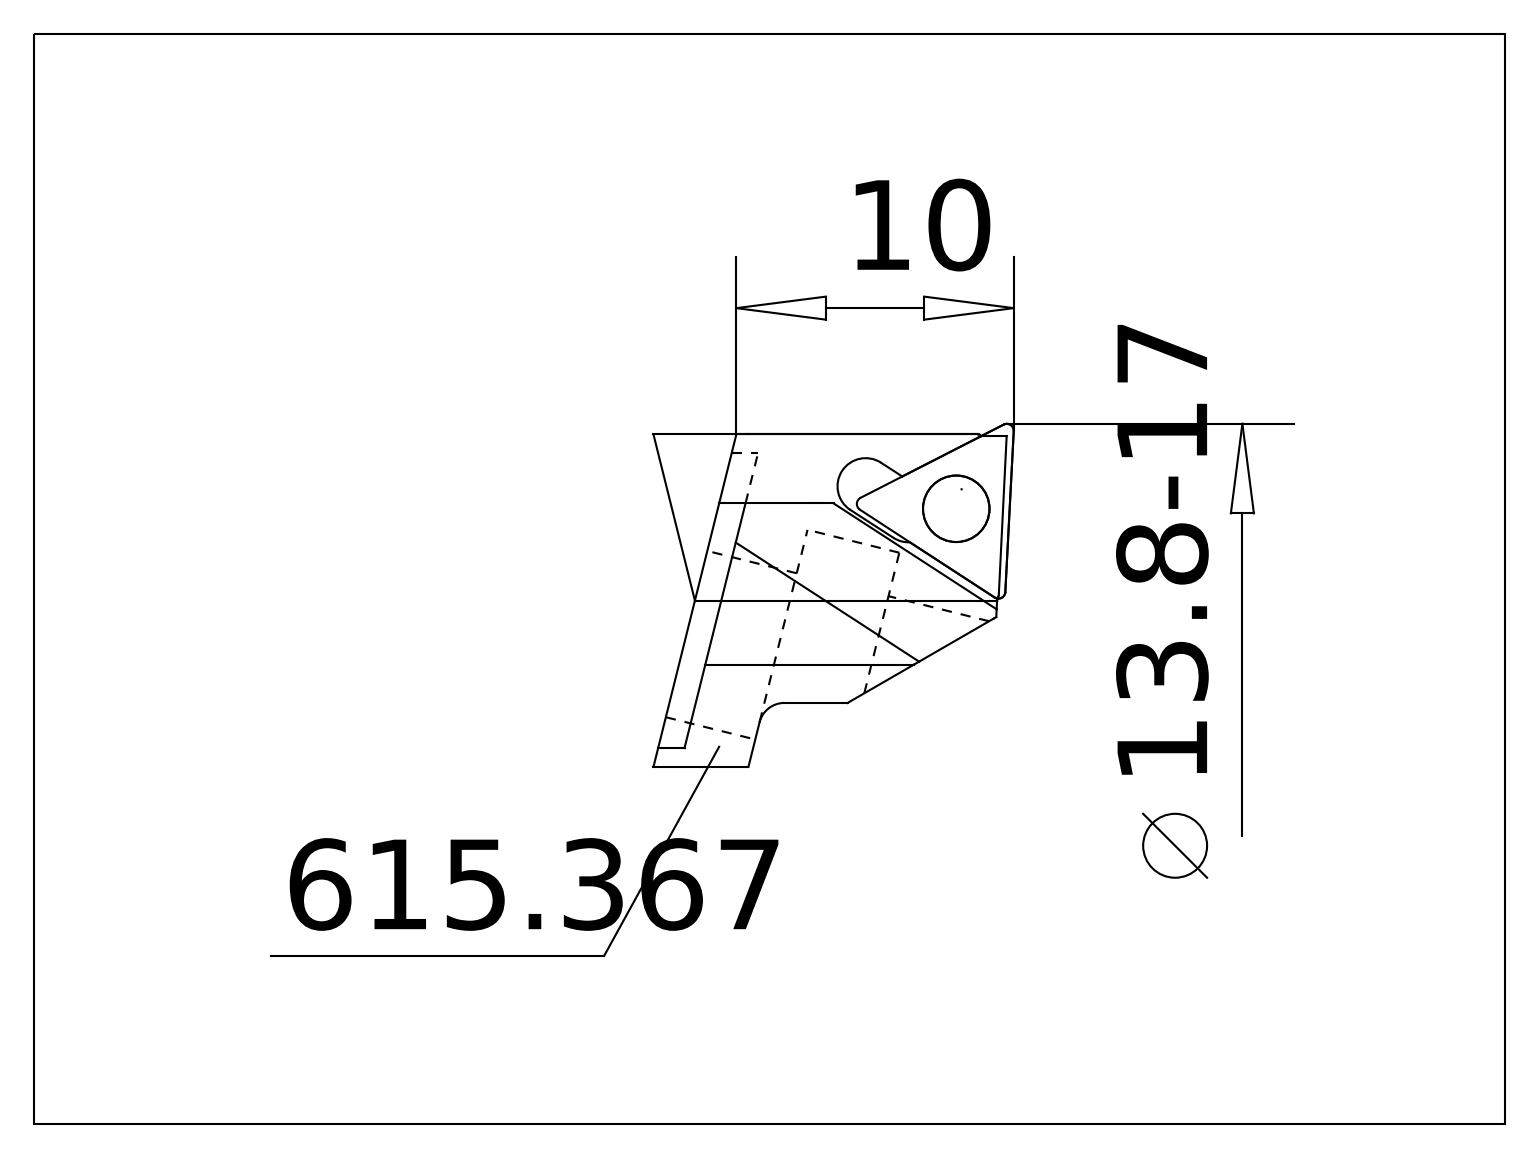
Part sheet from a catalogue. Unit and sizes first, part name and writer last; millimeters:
Units: millimetres
Overall size (bounding box): 14.54 × 13.44 × 12
Round holes (diameter × count): ⌀2.3 ×2, ⌀1.56 ×1
Round bosses / shafts (diameter × count): ⌀2.7 ×1, ⌀2 ×1
Partial cylindrical surfaces — rounded edges, fillets, slot ends (radius × count): R0.15 ×6, R0.3 ×6, R1.1 ×2, R2.6 ×2, R4.35 ×2, R1 ×1, R2.55 ×1, R6.5 ×1
Main face-to-face distances: 3, 6, 1, 4, 12, 9, 2.5, 1.65, 10.35, 1.35
Volume: 735 mm³ · Surface area: 1 121 mm²
Bodies: 5 solids, 151 faces (52 planar, 49 cylindrical, 50 other)
Part name (STEP PRODUCT): 615.367 Kaiser E14_17 TP07|694.103 Kaiser ETL M2x4.8 T6 IP 10S;Kreismuster1; 615.367 Kaiser E14_17 TP07|651.735 Kaiser TPGT 070203 K10C;Kombinieren1; 615.367 Kaiser E14_17 TP07|615.367 Kaiser E14_17 TP07-2;Fase1; 615.367 Kaiser E14_17 TP07|615.367 Kaiser E14_17 TP07-1;<N017.30 (TP 0702) PLS links Freistellung links>-<<0640.020>-<Schnitt-Linear austragen1>> (+1 more)
STEP written by: ACIS (automotive_design)
